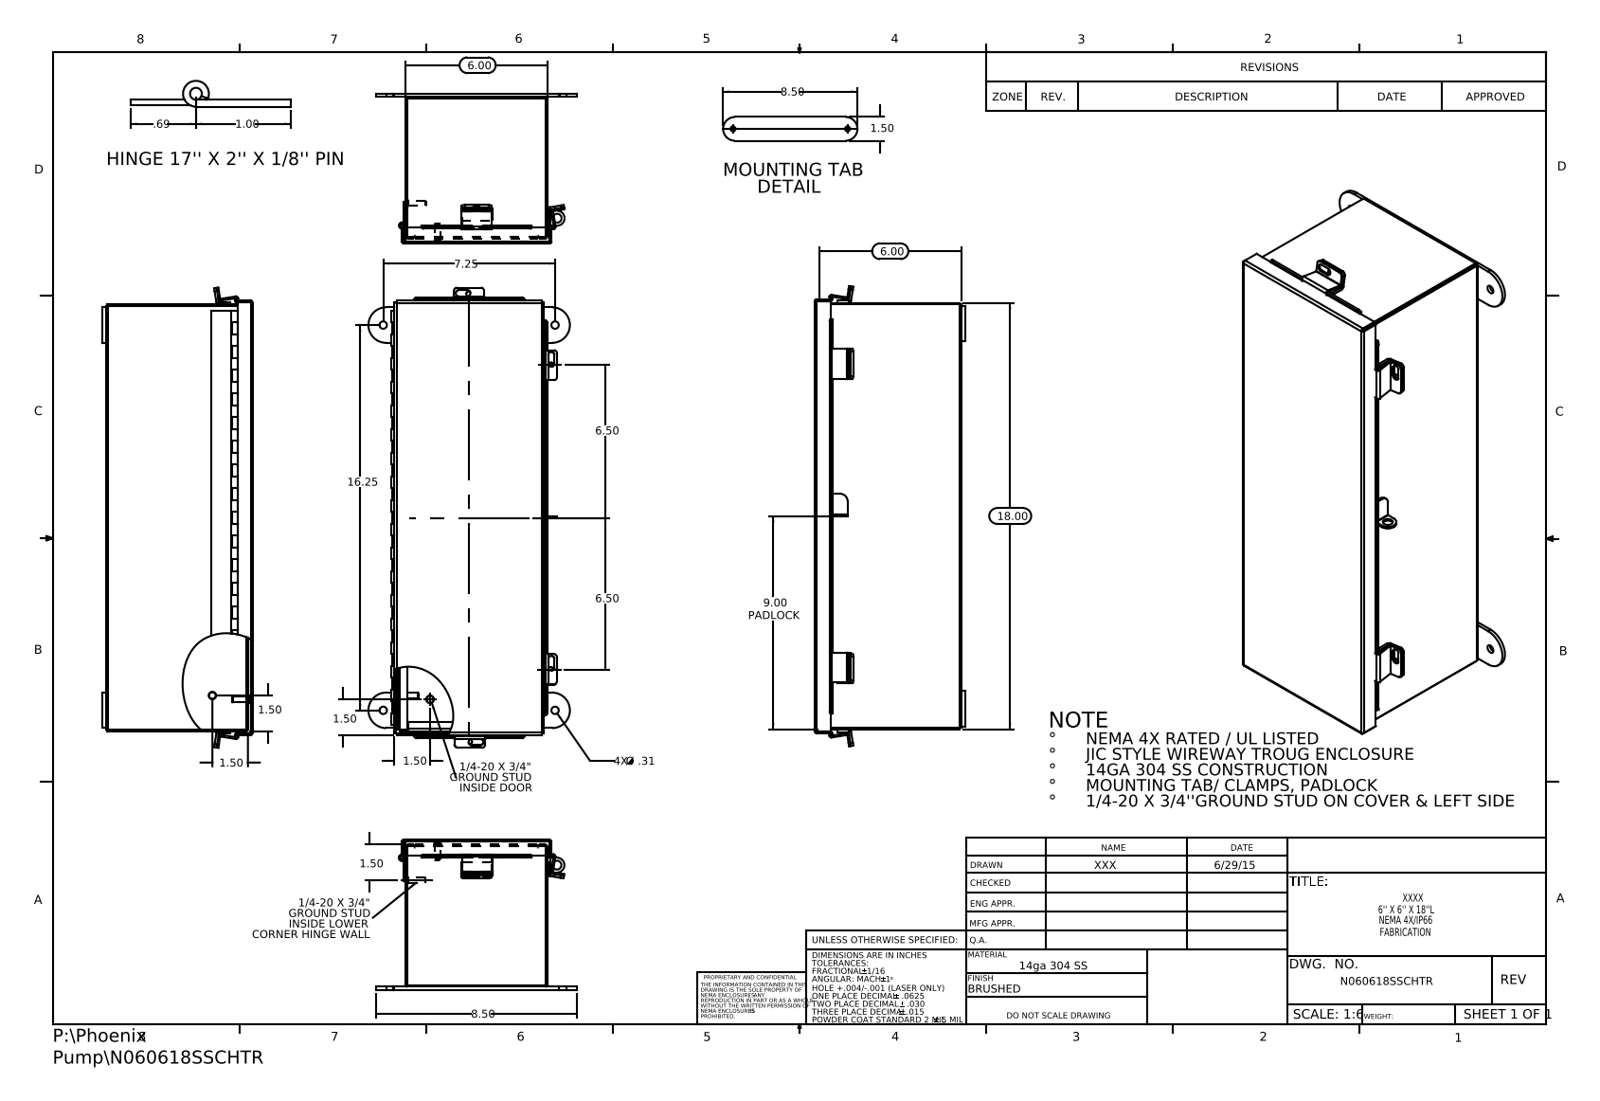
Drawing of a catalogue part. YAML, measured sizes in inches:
part_name: "N060618SSCHTR Hinge Cover Side JIC; N060618SSCHTR Hinge Body Side; N060618SSCHTR; N060618SSCHTR JIC Enclosure Template (+8 more)"
step_written_by: "SolidWorks 2015 (CONFIG_CONTROL_DESIGN)"
units: inches
bodies: {solids: 19, faces: 732, planar: 453, cylindrical: 259, other: 20}
overall_size: [19.407, 8.5, 6.337]
volume: 47.87
surface_area: 1275
round_holes:
  - {diameter: 0.25, count: 4}
  - {diameter: 0.313, count: 4}
  - {diameter: 0.125, count: 1}
  - {diameter: 0.375, count: 1}
round_bosses_or_shafts:
  - {diameter: 0.315, count: 2}
  - {diameter: 0.236, count: 2}
  - {diameter: 0.273, count: 1}
  - {diameter: 0.25, count: 1}
partial_cylinders:
  - {radius: 0.125, count: 14}
  - {radius: 0.009, count: 12}
  - {radius: 0.013, count: 11}
  - {radius: 0.088, count: 11}
  - {radius: 0.133, count: 8}
  - {radius: 0.083, count: 6}
  - {radius: 0.1, count: 6}
  - {radius: 0.75, count: 4}
face_to_face_distances: [0.075, 5.925, 6.128, 6, 5.85, 6.203, 6.053, 17.925, 0.149, 6.074]
hole_center_spacings: [7.25, 16.25, 17.794, 6.543, 12.85]
